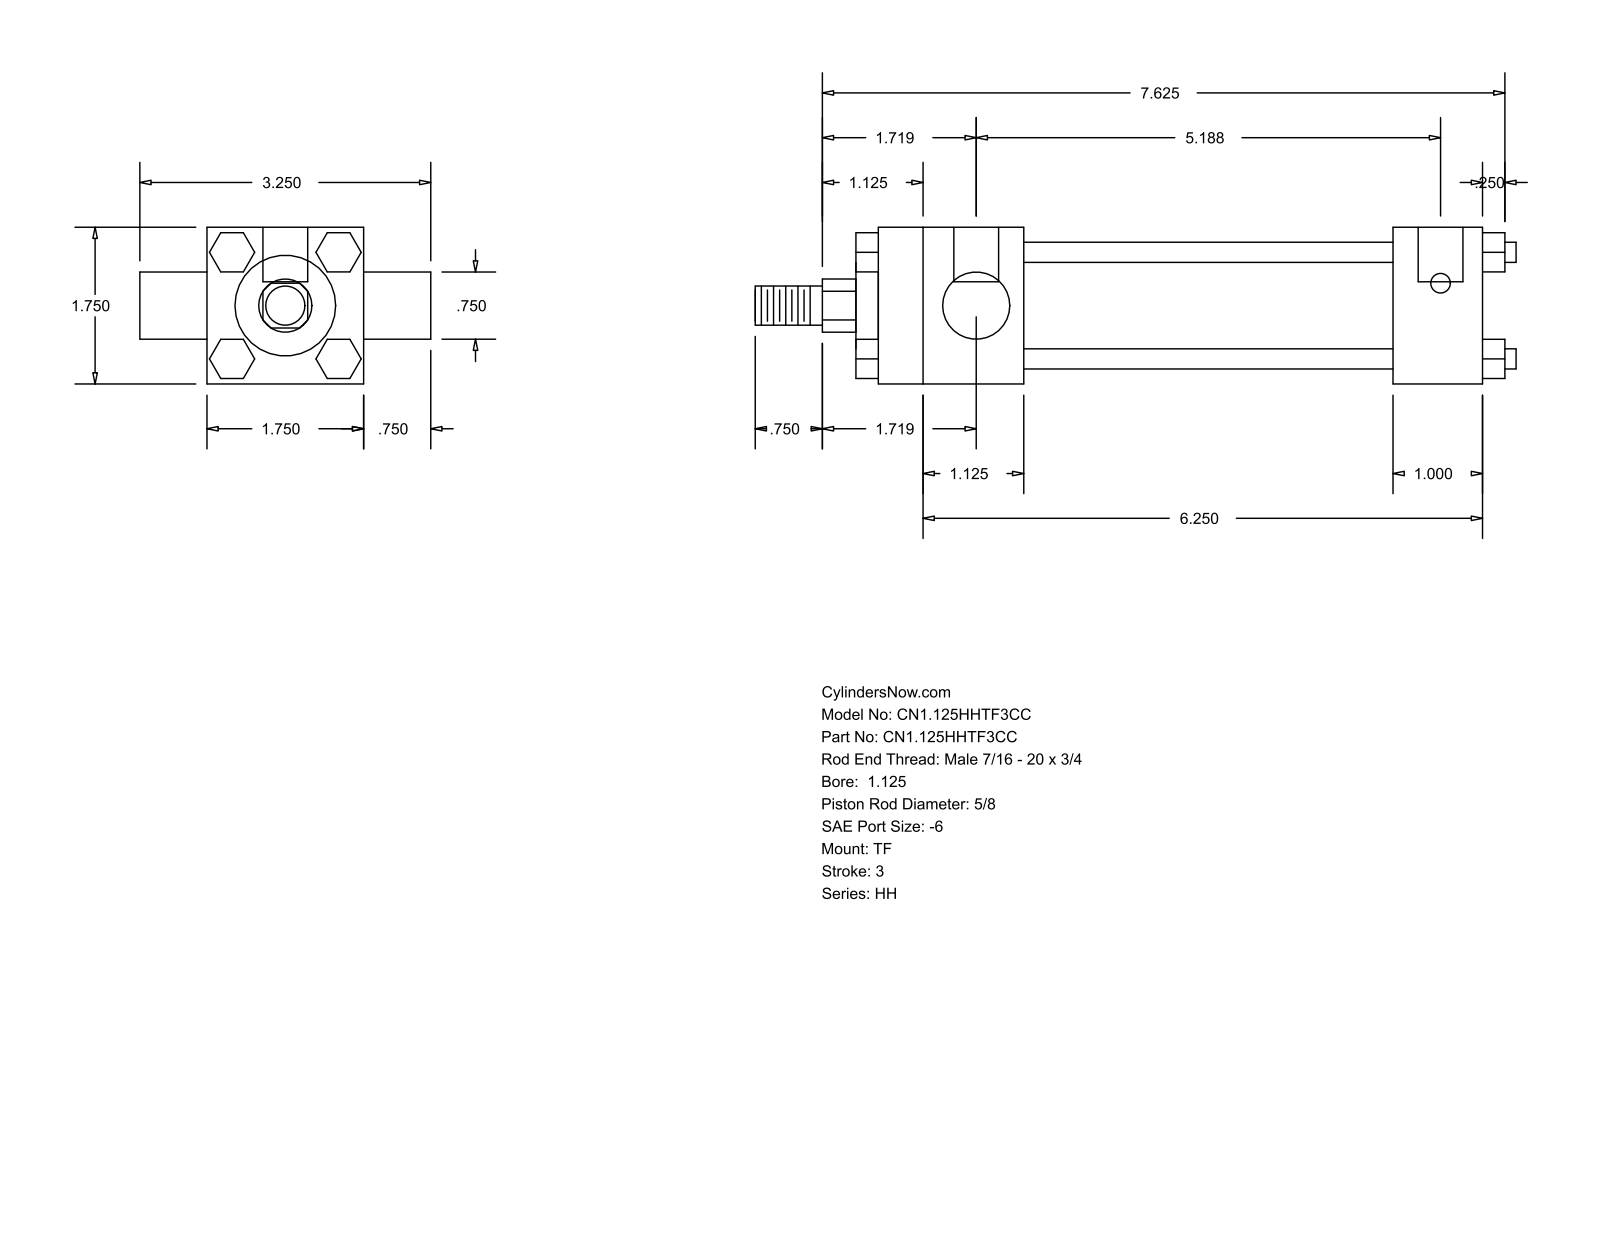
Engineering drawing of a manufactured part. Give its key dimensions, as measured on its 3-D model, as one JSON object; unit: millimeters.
{"part_name": "HH_TF__0112_0.625", "step_written_by": "GSSL Pune (CONFIG_CONTROL_DESIGN)", "units": "millimeters", "bodies": {"solids": 0, "faces": 120, "planar": 92, "cylindrical": 28, "other": 0}, "overall_size": [215.9, 82.55, 44.45], "round_holes": [[5.56, 3], [12.7, 2]], "round_bosses_or_shafts": [[5.71, 4], [34.92, 1], [28.57, 1], [19.05, 1], [15.88, 1], [11.11, 1]], "partial_cylinders_radius": [[7.54, 1]], "face_to_face_distances": [44.46, 11.11, 104.78, 130.17, 25.39, 41.27, 146.05, 171.44, 47.62, 6.35], "hole_center_spacings": [3.17, 128.59, 131.76]}
